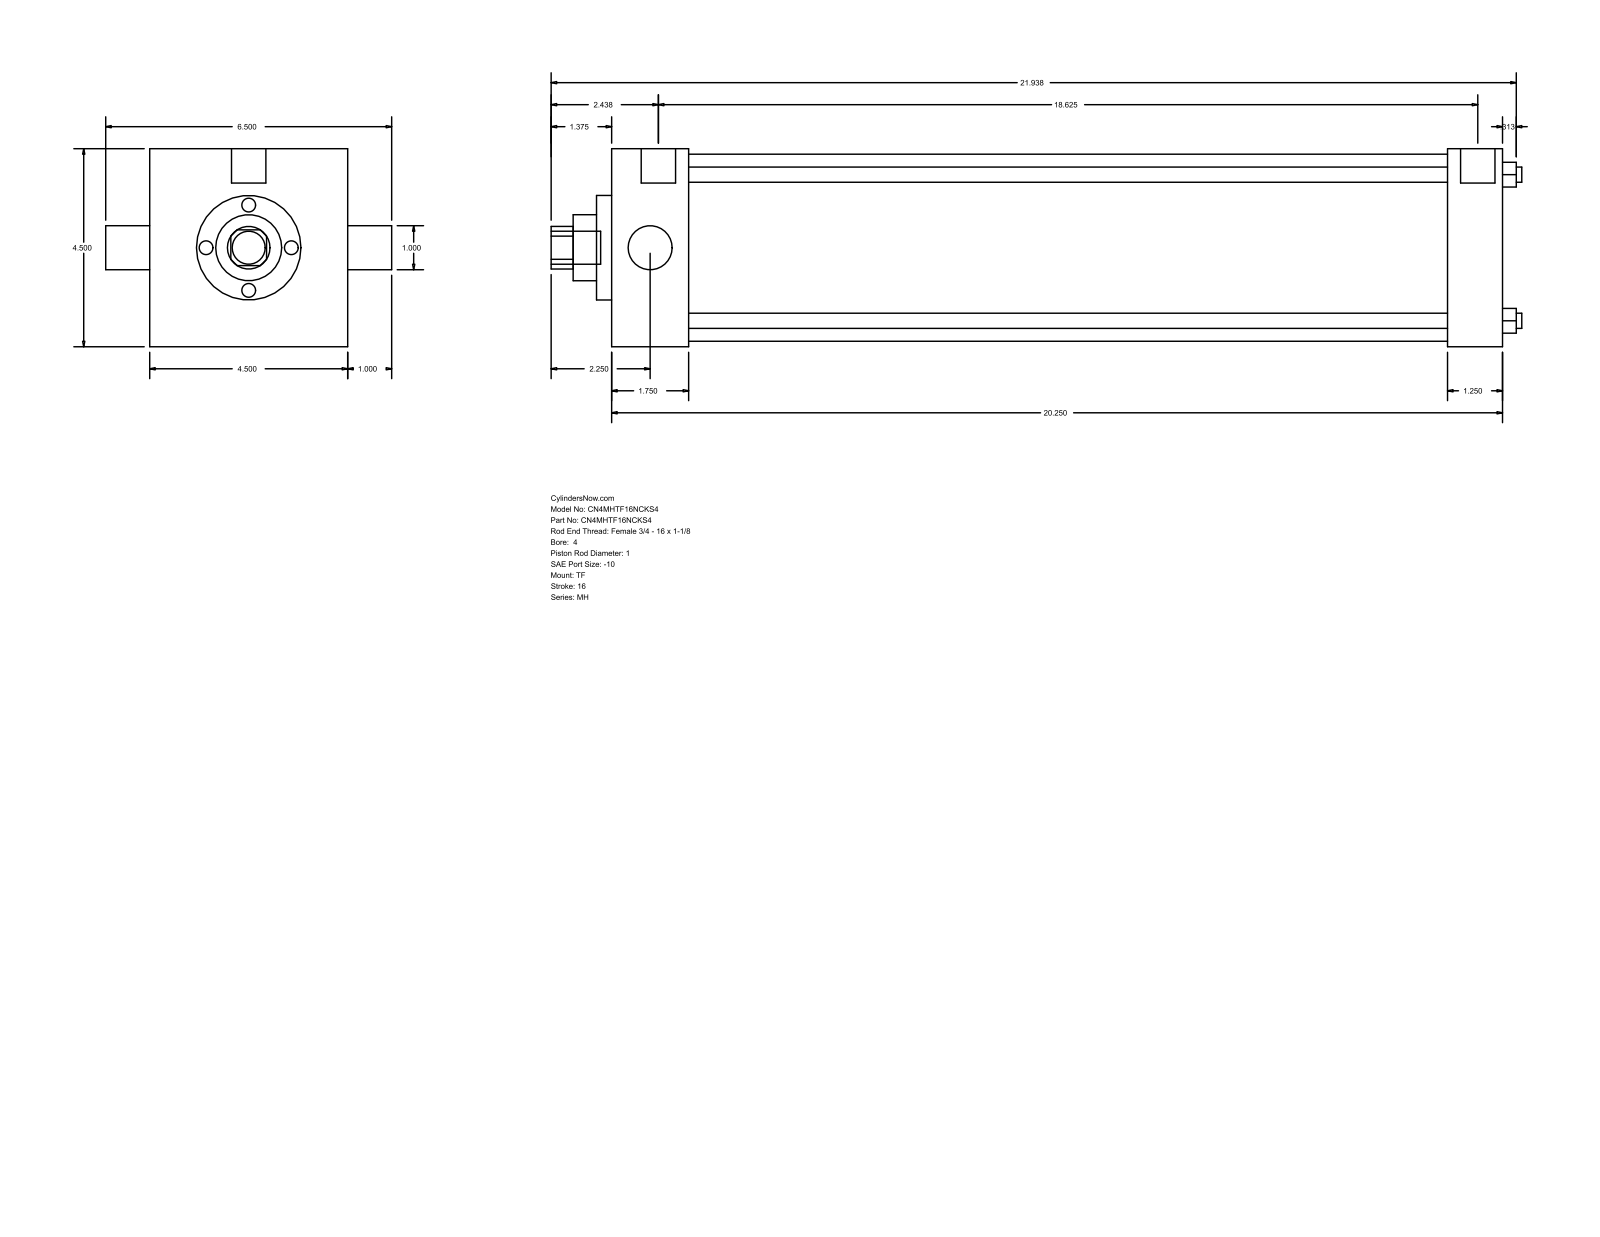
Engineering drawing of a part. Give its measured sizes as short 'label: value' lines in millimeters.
name: MH_TF__0400_1
written by: GSSL Pune (CONFIG_CONTROL_DESIGN)
unit: mm
bodies: 0 solids, 86 faces (61 planar, 25 cylindrical, 0 other)
size: 560.39 × 165.1 × 114.3
holes: 4× ⌀8.76, 2× ⌀25.4, 1× ⌀38.1, 1× ⌀60.33, 1× ⌀107.95
bosses: 3× ⌀8.73, 2× ⌀19.84, 1× ⌀19.05
rounds: 1× R12.29
face distances: 114.3, 514.35, 44.46, 469.89, 482.6, 438.14, 31.75, 8.73, 53.19, 491.33
hole spacings: 59.62, 84.32, 119.25
